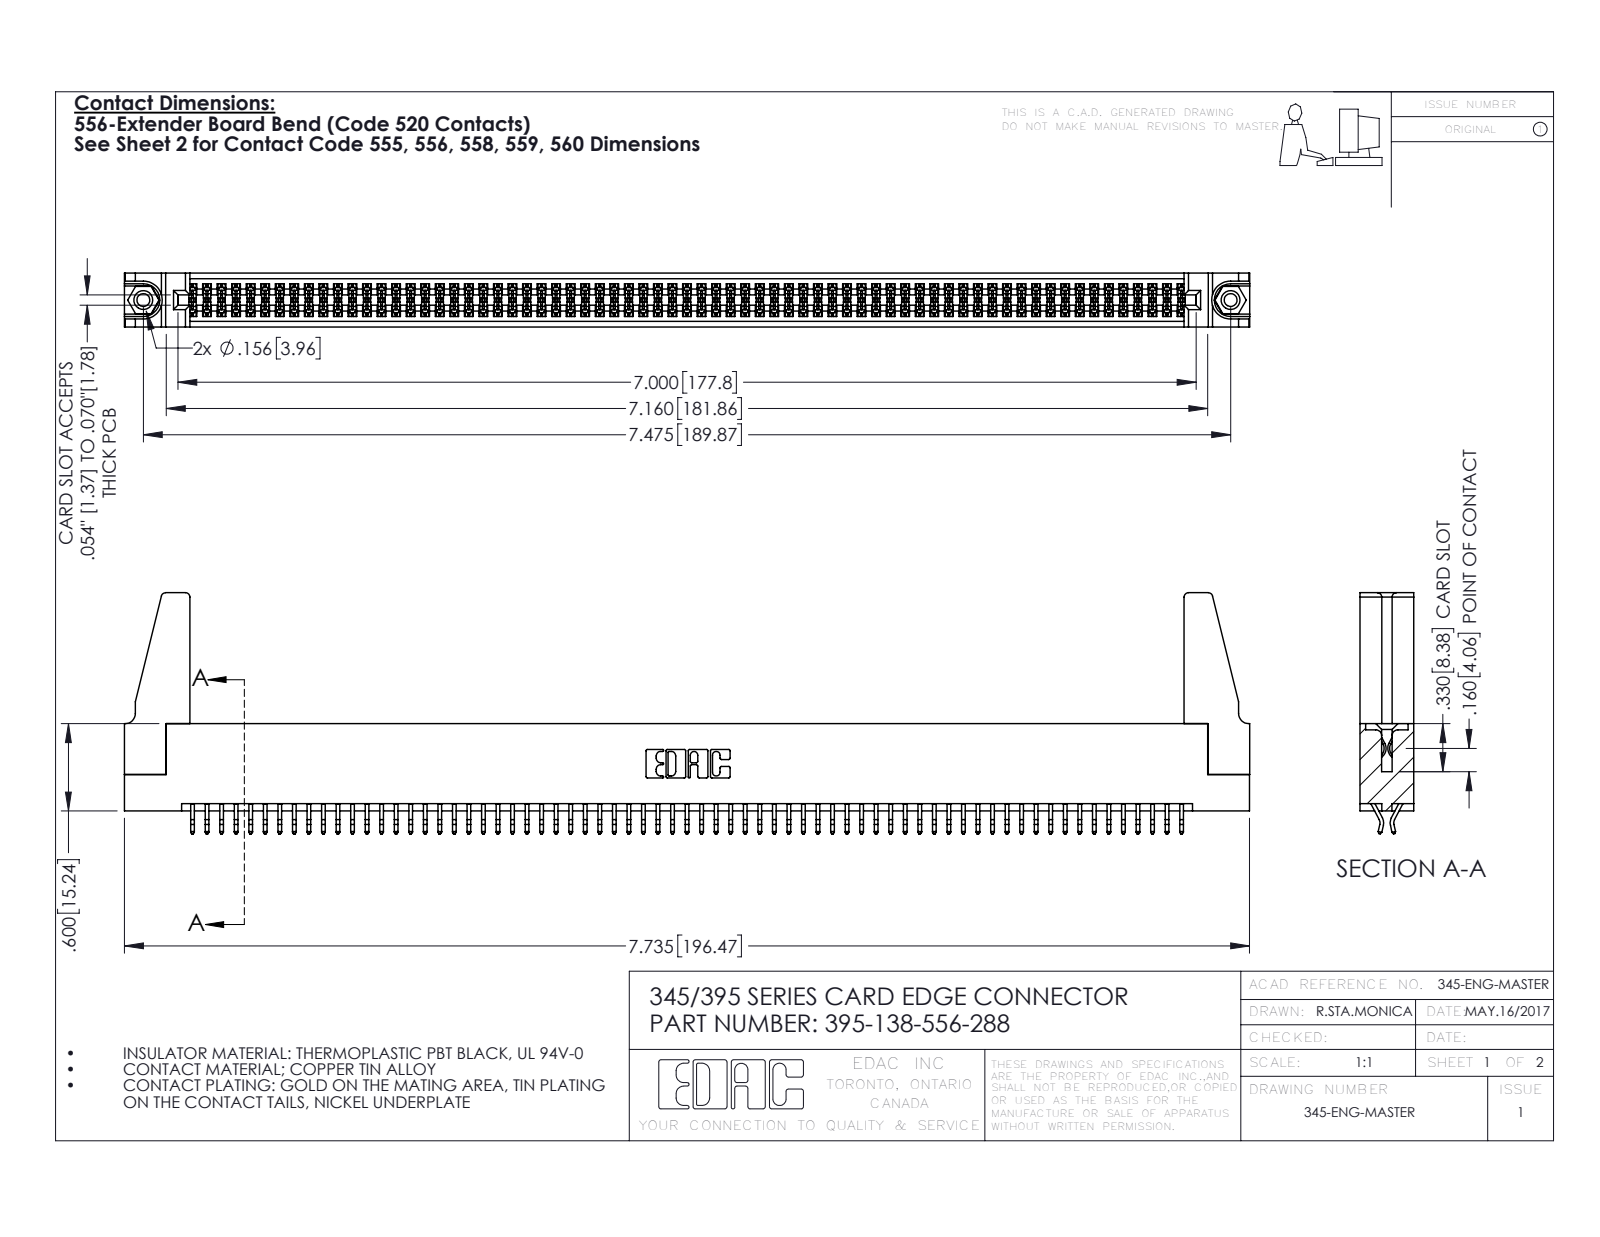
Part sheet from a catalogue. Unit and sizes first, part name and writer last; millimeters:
Units: millimetres
Overall size (bounding box): 196.5 × 42.1 × 9.4
Round holes (diameter × count): ⌀2.3 ×2, ⌀3.2 ×2, ⌀4 ×2, ⌀1.6 ×1
Round bosses / shafts (diameter × count): ⌀3.9 ×2
Partial cylindrical surfaces — rounded edges, fillets, slot ends (radius × count): R0.2 ×207, R0.3 ×22, R0.8 ×8, R0.2 ×6, R0.8 ×6, R0.7 ×3, R0.3 ×2, R0.4 ×2
Main face-to-face distances: 1.8, 7.6, 9.4, 5.1, 0.6, 2.5, 6.9, 5.7, 4.4, 3.8
Hole centre spacings: 6.9, 183.9, 189.9
Volume: 22 580 mm³ · Surface area: 32 100 mm²
Bodies: 143 solids, 7978 faces (5258 planar, 2704 cylindrical, 16 other)
Part name (STEP PRODUCT): 345-250-001_345-250-001-102; 395-138-556-288; 345-220-078_345-220-088; 345-292-001_556 Tail (+1 more)
STEP written by: SolidWorks 2016 (CONFIG_CONTROL_DESIGN)
